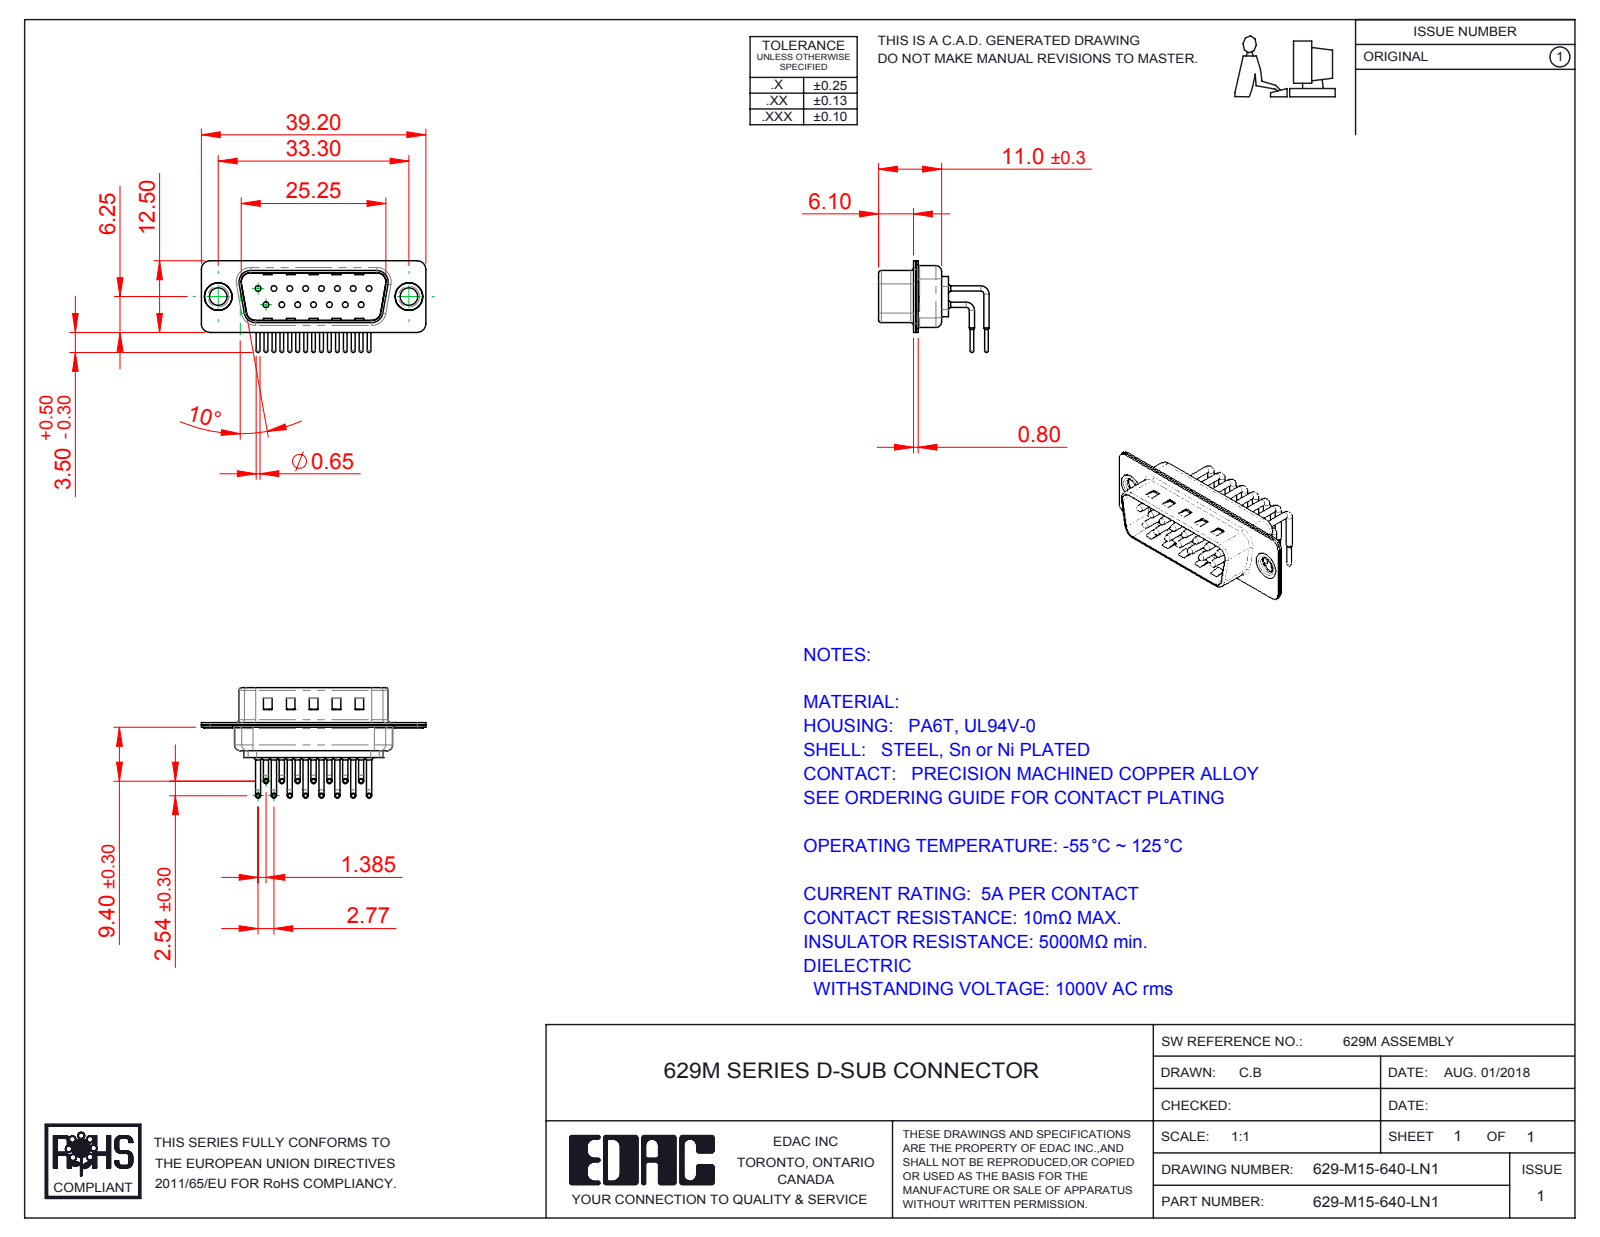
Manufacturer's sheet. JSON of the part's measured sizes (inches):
{"part_name": "629M Shell Front_15 Contacts; 629M Contact Row 1; 629M Thru Hole Rivet; 629M Shell Rear_15 Contacts (+3 more)", "step_written_by": "SolidWorks 2016 (CONFIG_CONTROL_DESIGN)", "units": "inches", "bodies": {"solids": 20, "faces": 1964, "planar": 1099, "cylindrical": 657, "other": 208}, "overall_size": [1.543, 0.759, 0.63], "volume_in3": 0.115, "surface_area_in2": 8.08, "round_holes": [[0.039, 15], [0.067, 15], [0.079, 15], [0.12, 2], [0.157, 2], [0.189, 2]], "round_bosses_or_shafts": [[0.035, 30], [0.059, 15], [0.026, 15], [0.197, 2], [0.193, 2], [0.14, 2]], "partial_cylinders_radius": [[0.059, 16], [0.04, 15], [0.079, 12], [0.02, 8], [0.063, 8], [0.01, 4], [0.024, 4], [0.026, 4]], "face_to_face_distances": [0.016, 0.033, 0.376, 0.343, 0.049, 0.031, 0.409, 0.059, 0.014, 0.075], "hole_center_spacings": [0.124, 0.109, 0.218, 0.327, 0.436, 0.198, 0.198, 0.294]}
